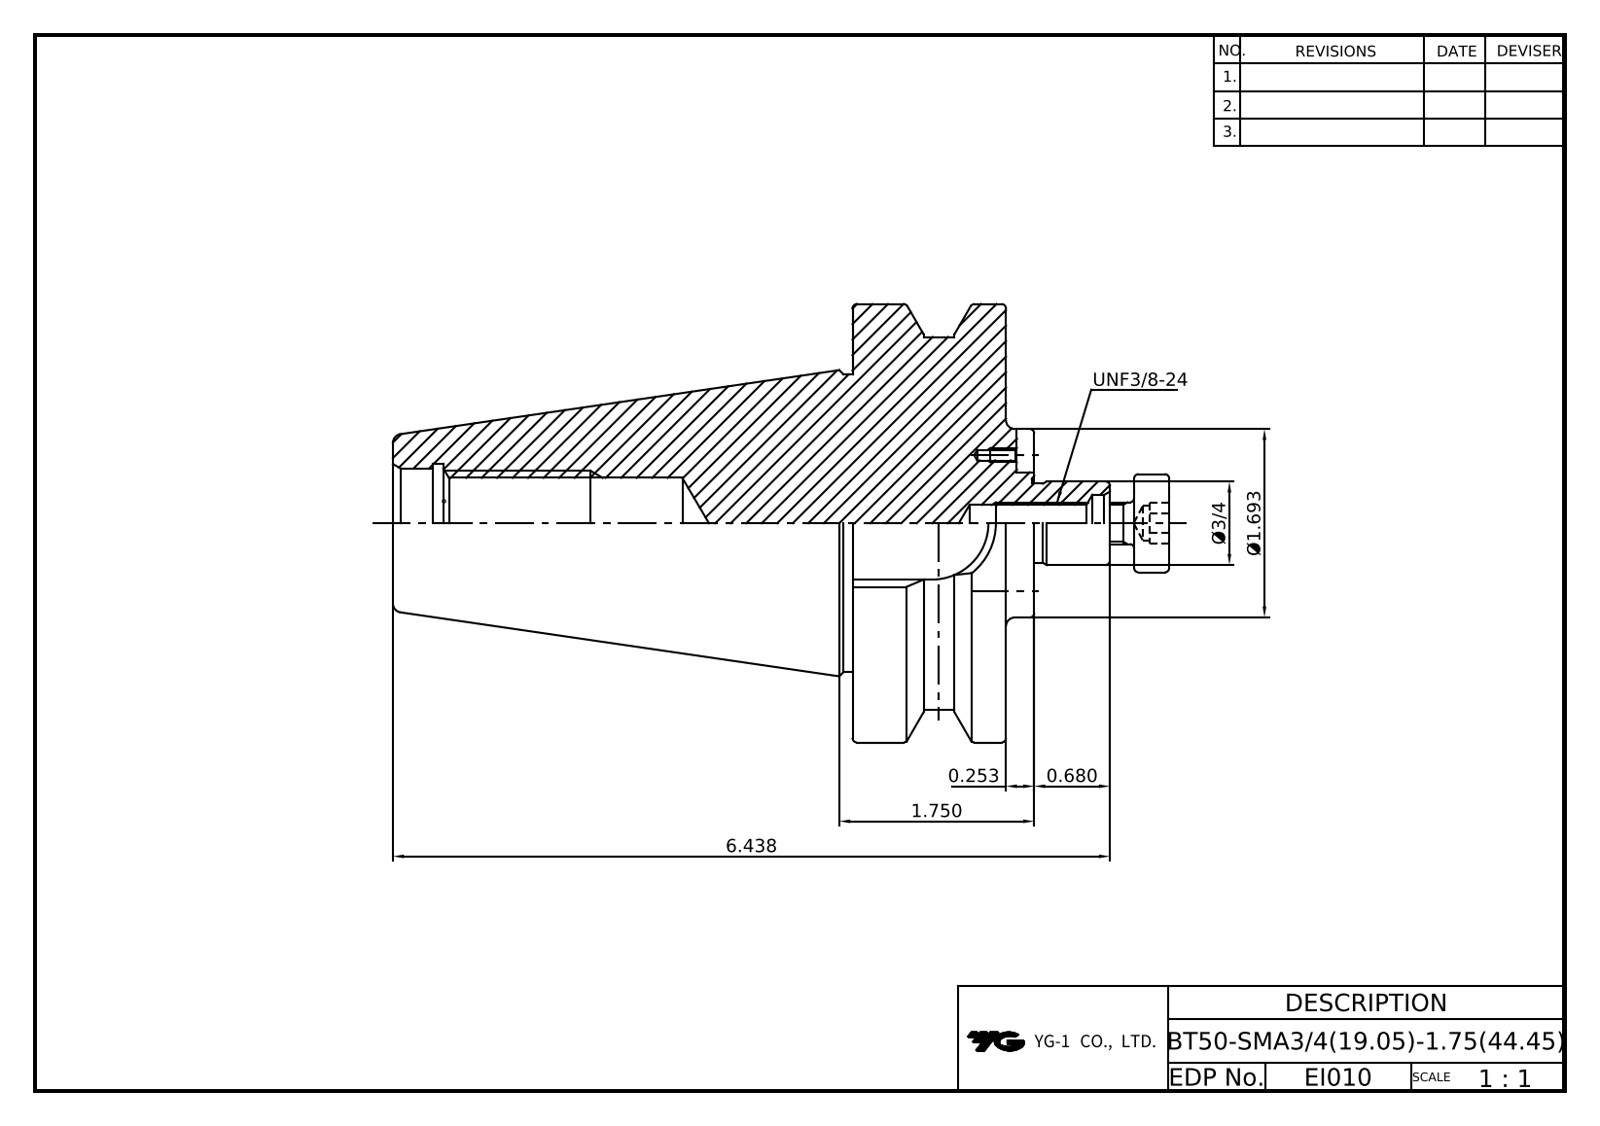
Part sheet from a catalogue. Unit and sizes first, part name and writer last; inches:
Units: inches
Overall size (bounding box): 6.95 × 3.937 × 3.937
Round holes (diameter × count): ⌀0.098 ×2, ⌀0.13 ×2, ⌀0.213 ×2, ⌀0.313 ×1, ⌀0.33 ×1, ⌀0.413 ×1, ⌀0.817 ×1, ⌀0.984 ×1, ⌀1.008 ×1
Round bosses / shafts (diameter × count): ⌀0.205 ×2, ⌀0.125 ×2, ⌀3.937 ×1, ⌀3.331 ×1, ⌀2.728 ×1, ⌀1.693 ×1, ⌀0.882 ×1, ⌀0.75 ×1
Partial cylindrical surfaces — rounded edges, fillets, slot ends (radius × count): R0.156 ×2, R0.506 ×1
Main face-to-face distances: 1.378, 1.632, 0.254, 2.787, 4.126, 5.504, 5.758, 1.012, 0.512, 6.438
Hole centre spacings: 0.611, 1.222
Volume: 28.75 in³ · Surface area: 91.57 in²
Bodies: 6 solids, 129 faces (68 planar, 32 cylindrical, 29 other)
Part name (STEP PRODUCT): LO-BT50-SMA19.05-44.45; DRIVE KEY-7.93x7.93x9.5; HEX'' WRENCH BOLT-UNC#5-40x5_16L; COLLAR BOLT-UNF3_8-24x24L
STEP written by: Autodesk Inventor 2026 (AUTOMOTIVE_DESIGN)
